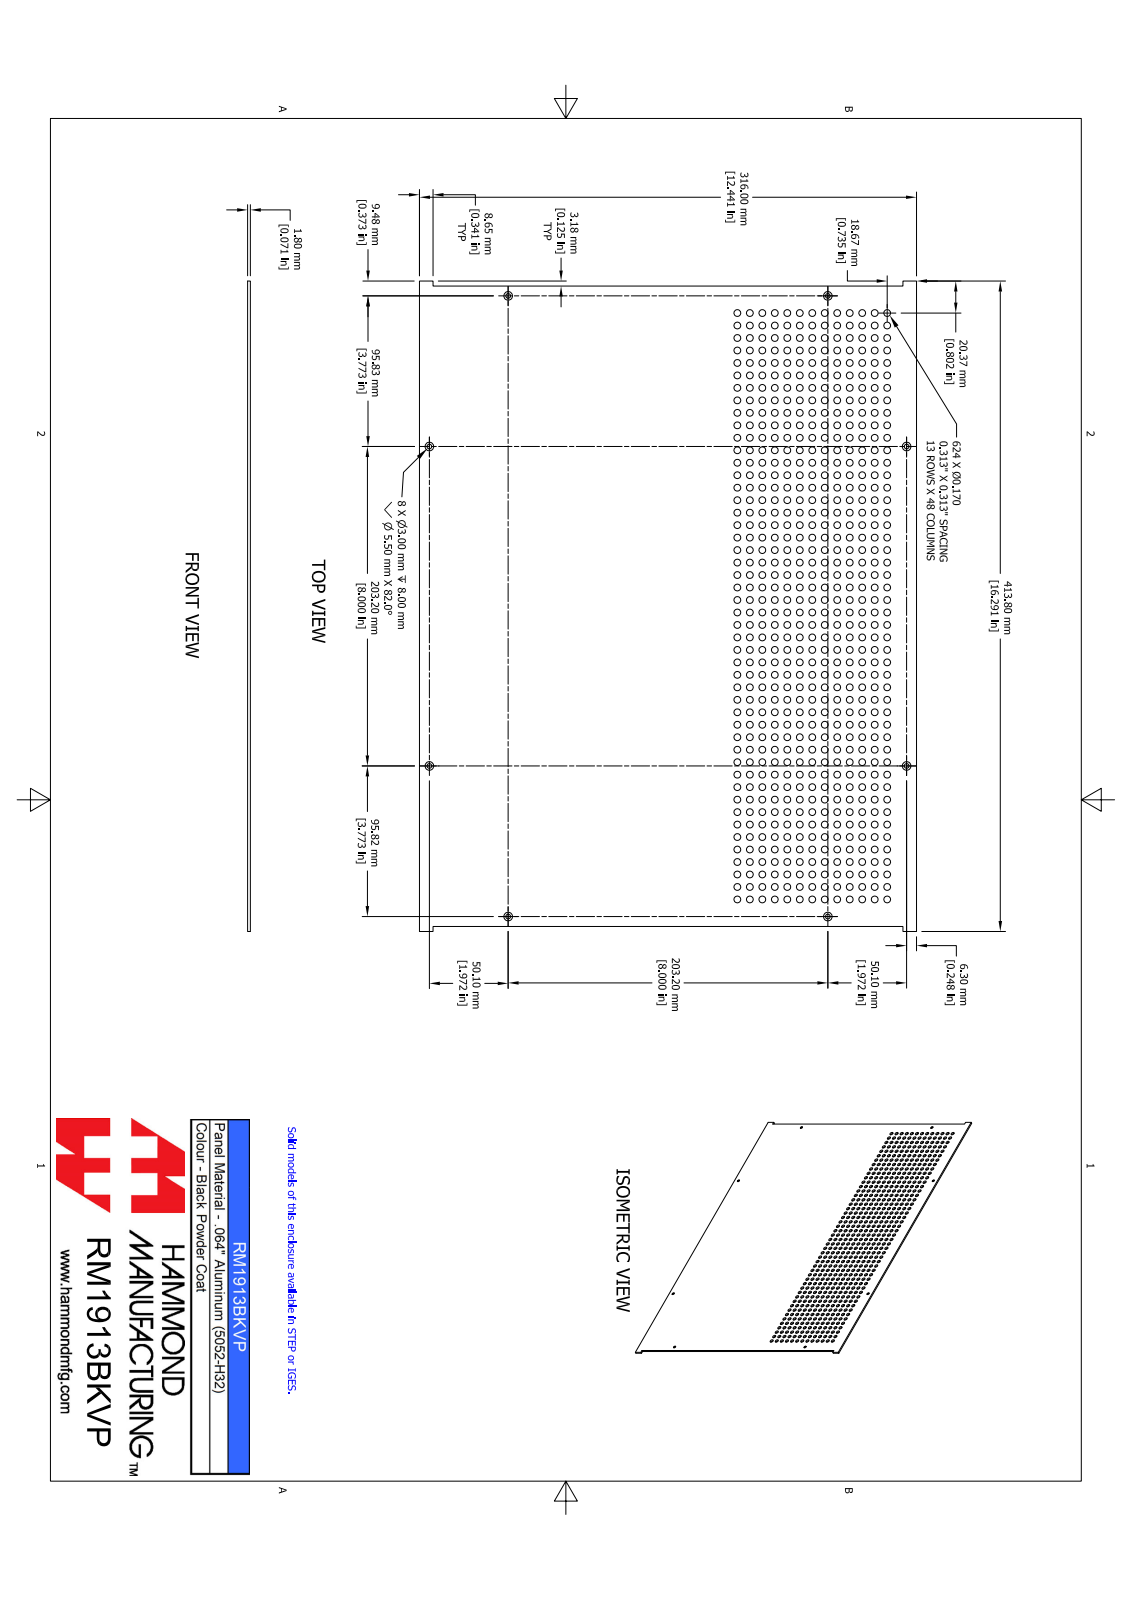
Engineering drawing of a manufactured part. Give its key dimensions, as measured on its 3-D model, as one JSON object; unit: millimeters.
{"part_name": "RM1913BKVP", "step_written_by": "SolidWorks 2021 (AUTOMOTIVE_DESIGN)", "units": "millimeters", "bodies": {"solids": 1, "faces": 654, "planar": 14, "cylindrical": 632, "other": 8}, "overall_size": [413.8, 316, 1.8], "volume_mm3": 215300, "surface_area_mm2": 257400, "round_holes": [[4.3, 624], [3, 8]], "face_to_face_distances": [1.8, 316, 407.4, 410.6, 3.2, 3.2, 410.6, 413.8, 8.7, 307.3], "hole_center_spacings": [31.8, 8, 23.8, 63.5, 39.7, 55.5, 15.9, 15.9]}
